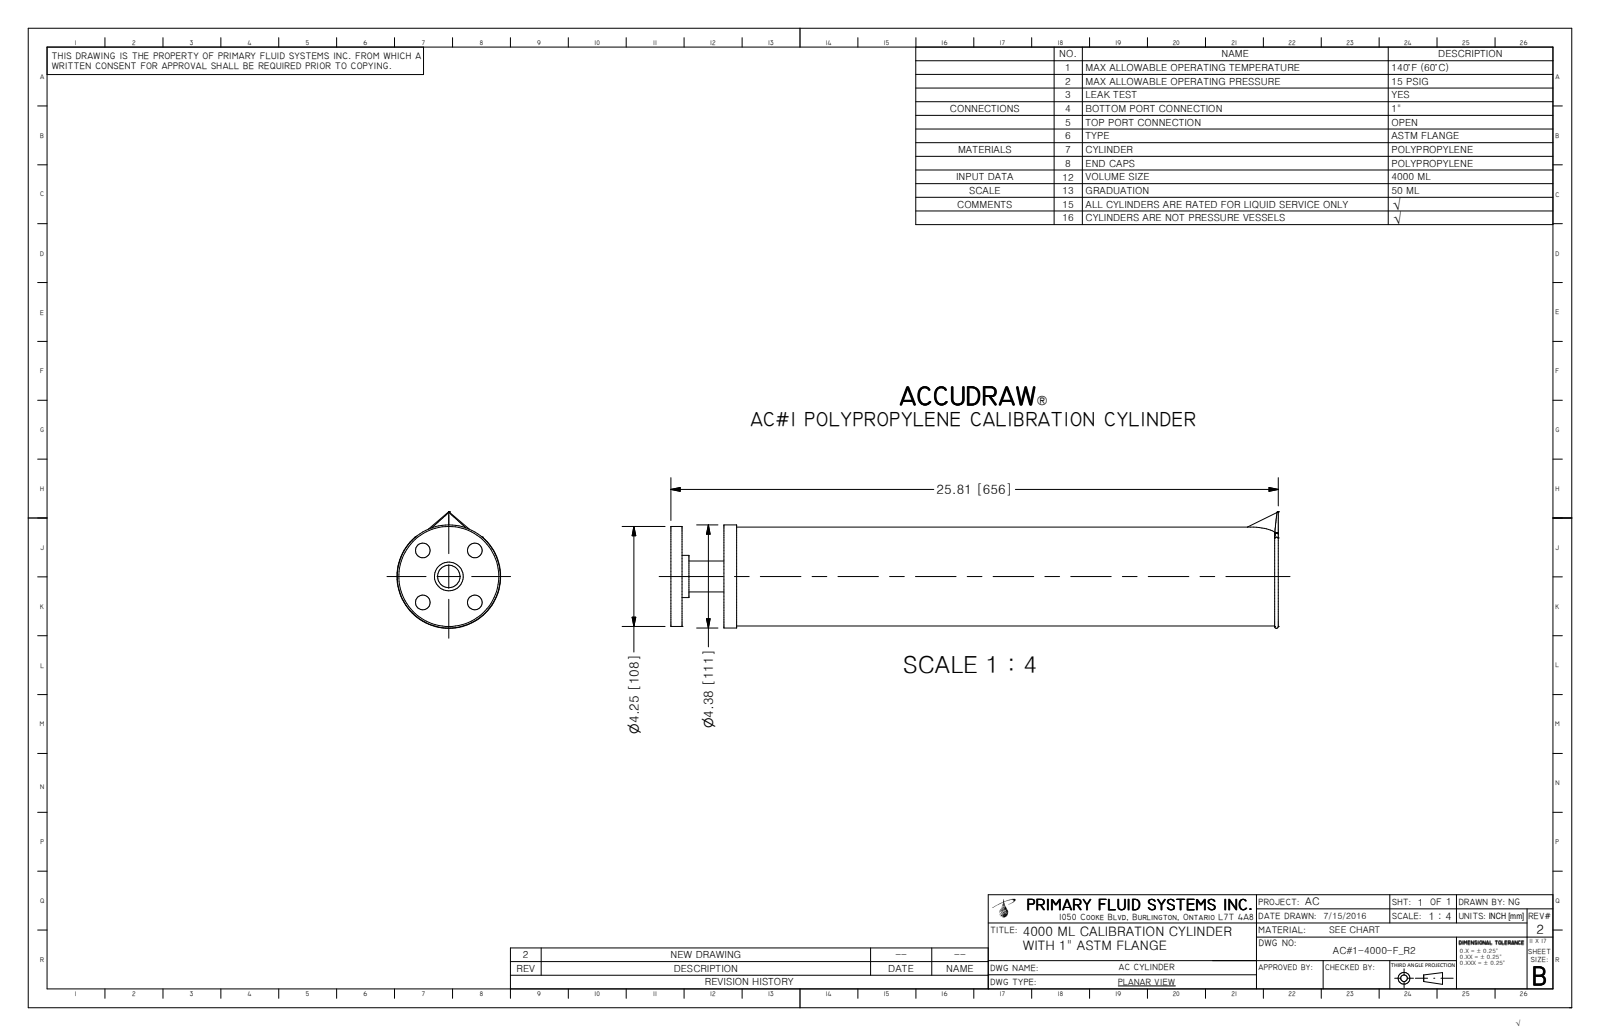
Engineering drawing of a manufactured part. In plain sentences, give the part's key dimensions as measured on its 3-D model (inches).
The part is named "AC#1-4000-F_R2; SA-10FLG-PP_R0; FLG-10PP_R0; PIPE-10PP-SCH80 (+2 more)". Its 3-D file was written by "Autodesk Inventor 2009 (AUTOMOTIVE_DESIGN)". It is 4 solids with 40 faces: 17 planar, 15 cylindrical and 8 other. Overall it measures 25.809 by 4.949 by 4.404 inches. Its volume is 59.42 cubic inches and its surface area 691.3 square inches. Round holes: 4 of diameter 0.622, 1 of diameter 0.953, 1 of diameter 1.125, 1 of diameter 1.222, 1 of diameter 1.311, 1 of diameter 3.913. Round bosses or shafts: 1 of diameter 4.38, 1 of diameter 4.25, 1 of diameter 4.2, 1 of diameter 3.95, 1 of diameter 1.79. The main face-to-face distances are 2.25, 3, 0.75, 0.47, 1.78, 2.53, 2.79, 2.32, 0.54, 0.21. The hole center spacings are 1.562, 2.209, 1.563, 3.125.
